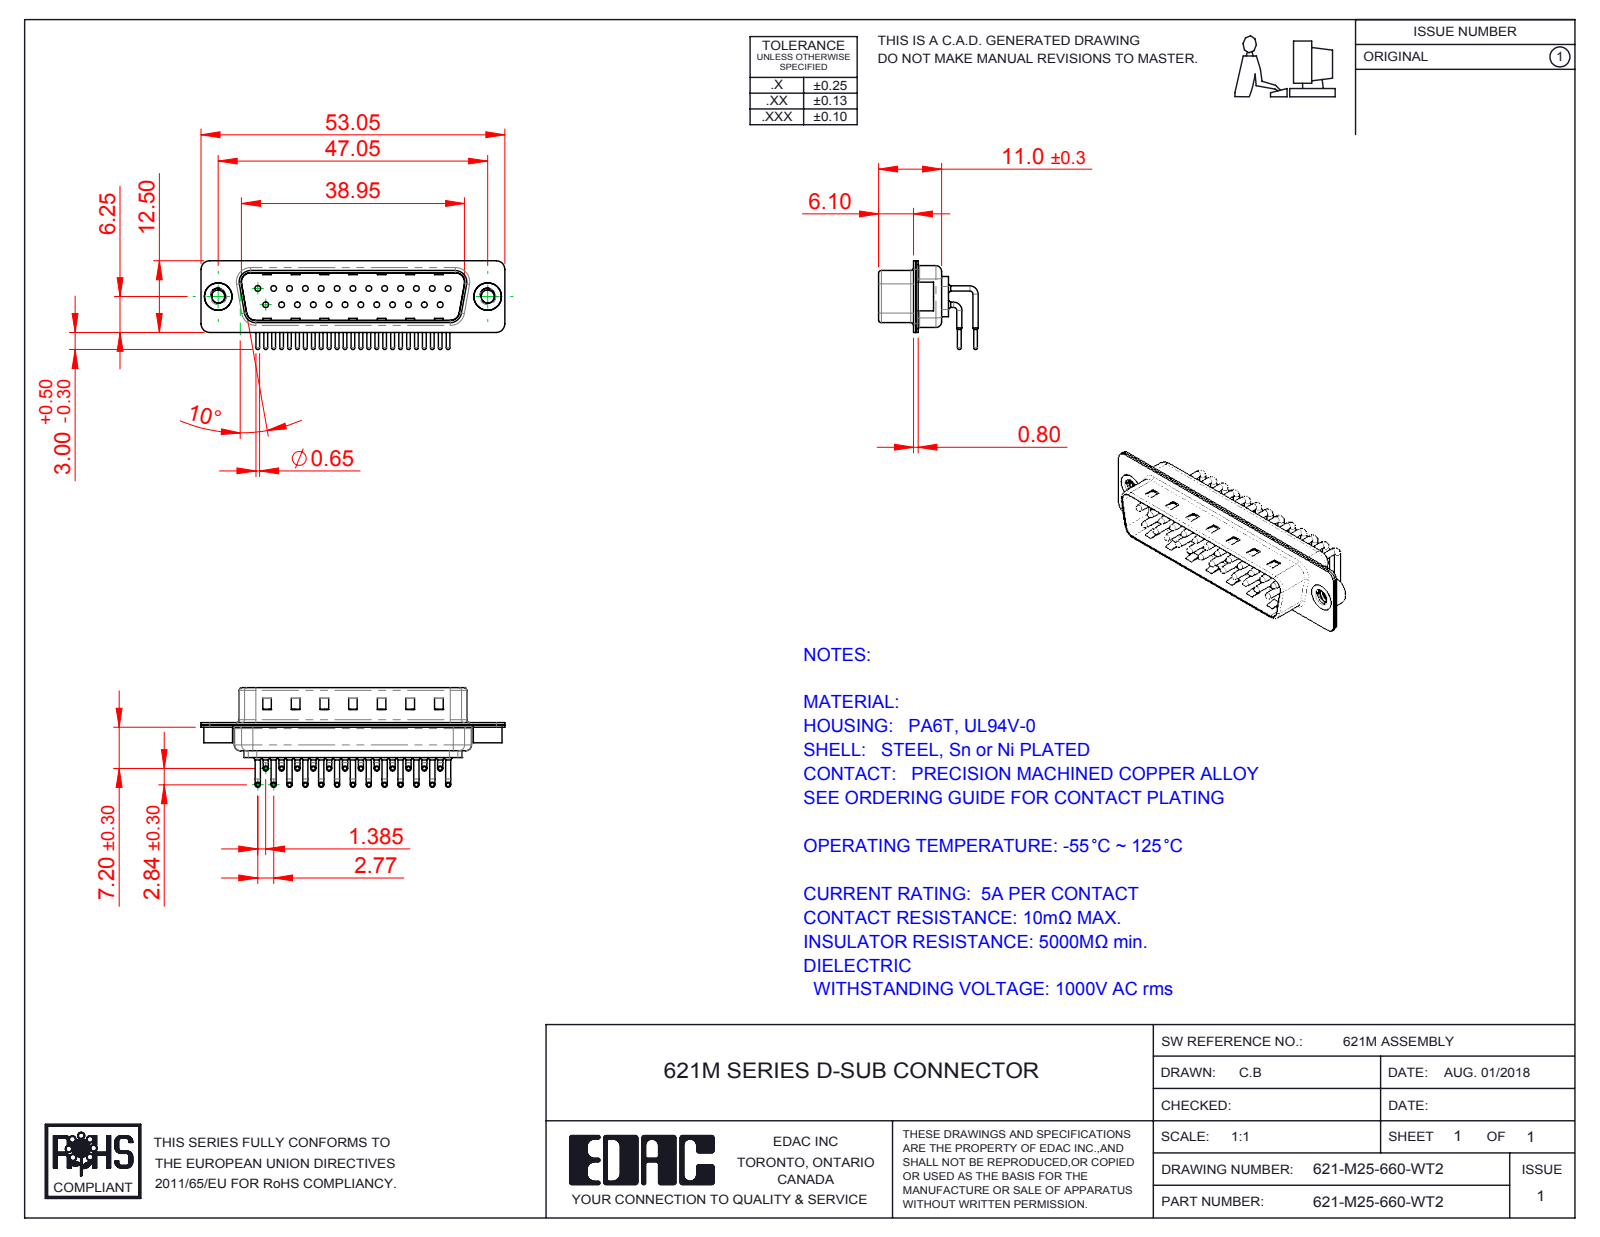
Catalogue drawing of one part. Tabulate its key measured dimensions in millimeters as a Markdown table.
| quantity | value |
| --- | --- |
| part name | 621M Shell Front_25 Contacts; 621M Housing_25 Contacts; 621M Contact Row 1; 621M Contact Row 2 (+3 more) |
| STEP written by | SolidWorks 2016 (CONFIG_CONTROL_DESIGN) |
| units | millimeters |
| bodies | 30 solids, 3126 faces (1771 planar, 1037 cylindrical, 318 other) |
| overall size | 53.05 × 17.39 × 15.49 |
| volume | 2 875 mm³ |
| surface area | 7 590 mm² |
| round holes (diameter × count) | 1 × 25, 1.7 × 25, 2 × 25, 2.26 × 2, 4 × 2, 4.8 × 2 |
| round bosses / shafts (diameter × count) | 0.9 × 50, 1.5 × 25, 0.65 × 25, 5 × 2, 4.9 × 2 |
| partial cylindrical surfaces (radius × count) | 1.01 × 25, 1.5 × 16, 2 × 12, 0.5 × 8, 1.6 × 8, 0.25 × 4, 0.6 × 4, 0.65 × 4 |
| main face-to-face distances | 0.4, 0.85, 9.55, 8.7, 1.25, 10.4, 1.5, 1.9, 0.35, 6.1 |
| hole center spacings | 3.16, 8.31, 2.77, 5.54, 11.08, 16.62, 5.03, 5.04 |
